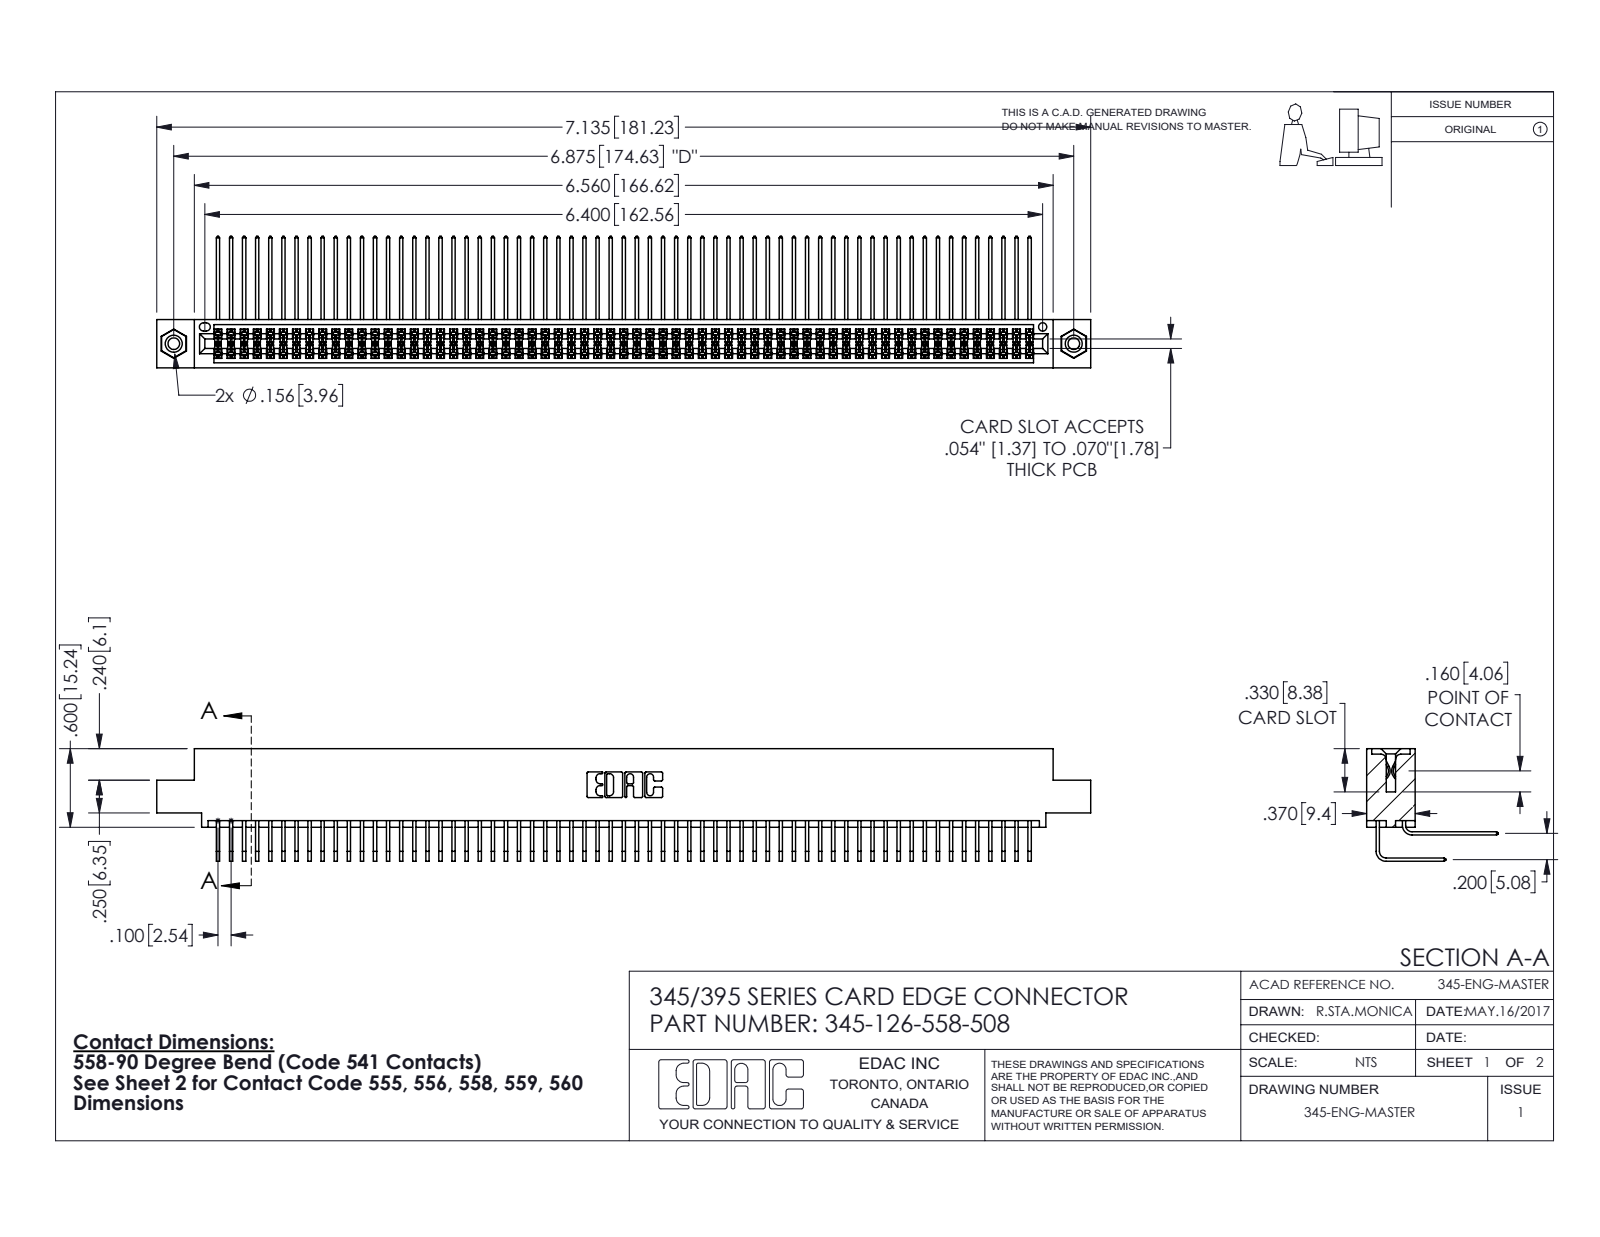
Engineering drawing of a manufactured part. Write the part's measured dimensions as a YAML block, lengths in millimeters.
part_name: "345-292-001_558 559 Tail - 1; 345-126-558-508; 345-292-001_558 Tail - 2; 345 Part_0.110 Offset - 0.156 Dia-TI (+1 more)"
step_written_by: "SolidWorks 2016 (CONFIG_CONTROL_DESIGN)"
units: millimeters
bodies: {solids: 129, faces: 6742, planar: 4526, cylindrical: 2200, other: 16}
overall_size: [181.2, 25.5, 21.8]
volume: 18450
surface_area: 31200
round_holes:
  - {diameter: 2.3, count: 2}
  - {diameter: 3.2, count: 2}
  - {diameter: 4, count: 2}
  - {diameter: 1.6, count: 1}
round_bosses_or_shafts:
  - {diameter: 3.9, count: 2}
partial_cylinders:
  - {radius: 0.2, count: 252}
  - {radius: 0.3, count: 22}
  - {radius: 0.2, count: 6}
  - {radius: 0.8, count: 6}
  - {radius: 0.7, count: 3}
  - {radius: 0.4, count: 2}
  - {radius: 0.5, count: 2}
  - {radius: 0.6, count: 2}
face_to_face_distances: [1.8, 7.6, 5.1, 9.4, 2.5, 6.9, 0.6, 5.7, 0.6, 4.4]
hole_center_spacings: [6.9, 168.6, 174.6]
